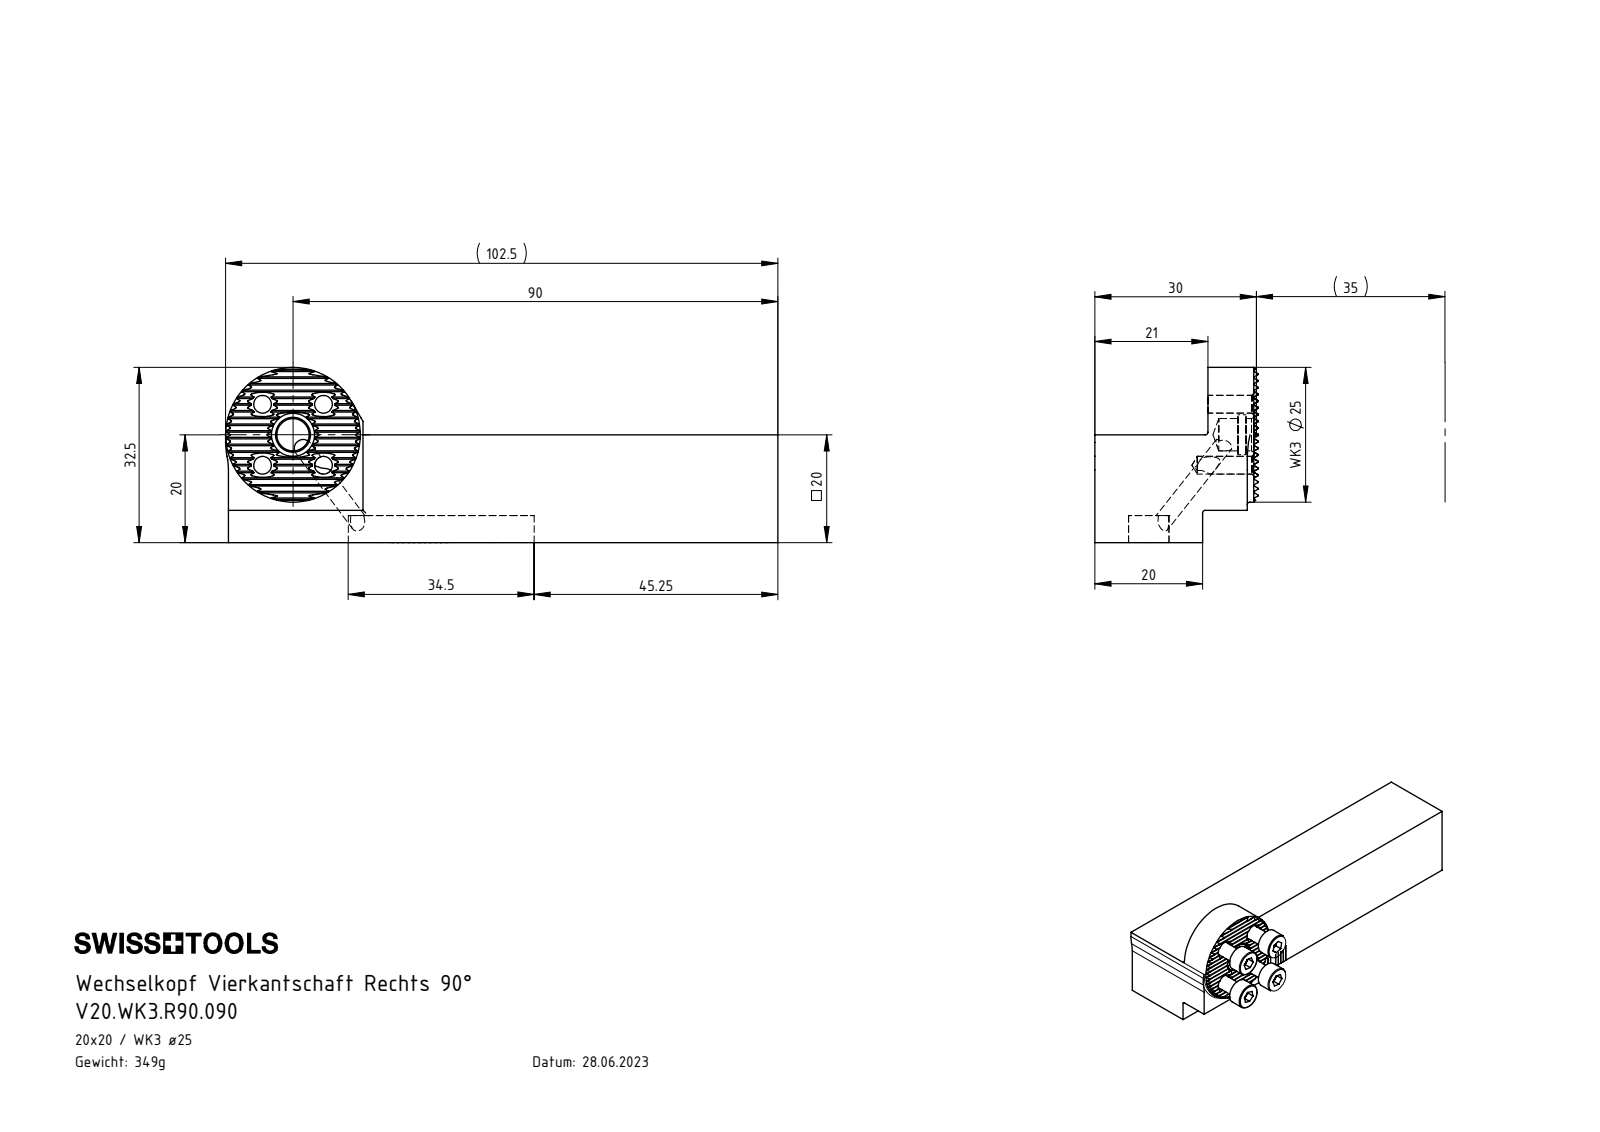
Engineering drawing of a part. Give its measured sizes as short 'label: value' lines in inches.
name: V20-WK3.R90.090_A; ISO 4762 - M4 x 12; DIN 3771 - 6x1; V20.WK3.R90.090
written by: SolidWorks 2017 (AUTOMOTIVE_DESIGN)
unit: in
bodies: 5 solids, 373 faces (201 planar, 122 cylindrical, 50 other)
size: 4.035 × 1.555 × 1.28
volume: 2.761 in³; area: 19.61 in²
holes: 5× ⌀0.13, 1× ⌀0.236, 1× ⌀0.291
bosses: 3× ⌀0.276, 3× ⌀0.157, 1× ⌀0.984
rounds: 19× R0.005, 3× R0.02, 2× R0.148, 2× R0.512
face distances: 0.787, 0.039, 4.016, 0.17, 0.246, 0.541, 0.043, 0.197, 0.591, 0.236
hole spacings: 0.315, 0.446, 0.63
